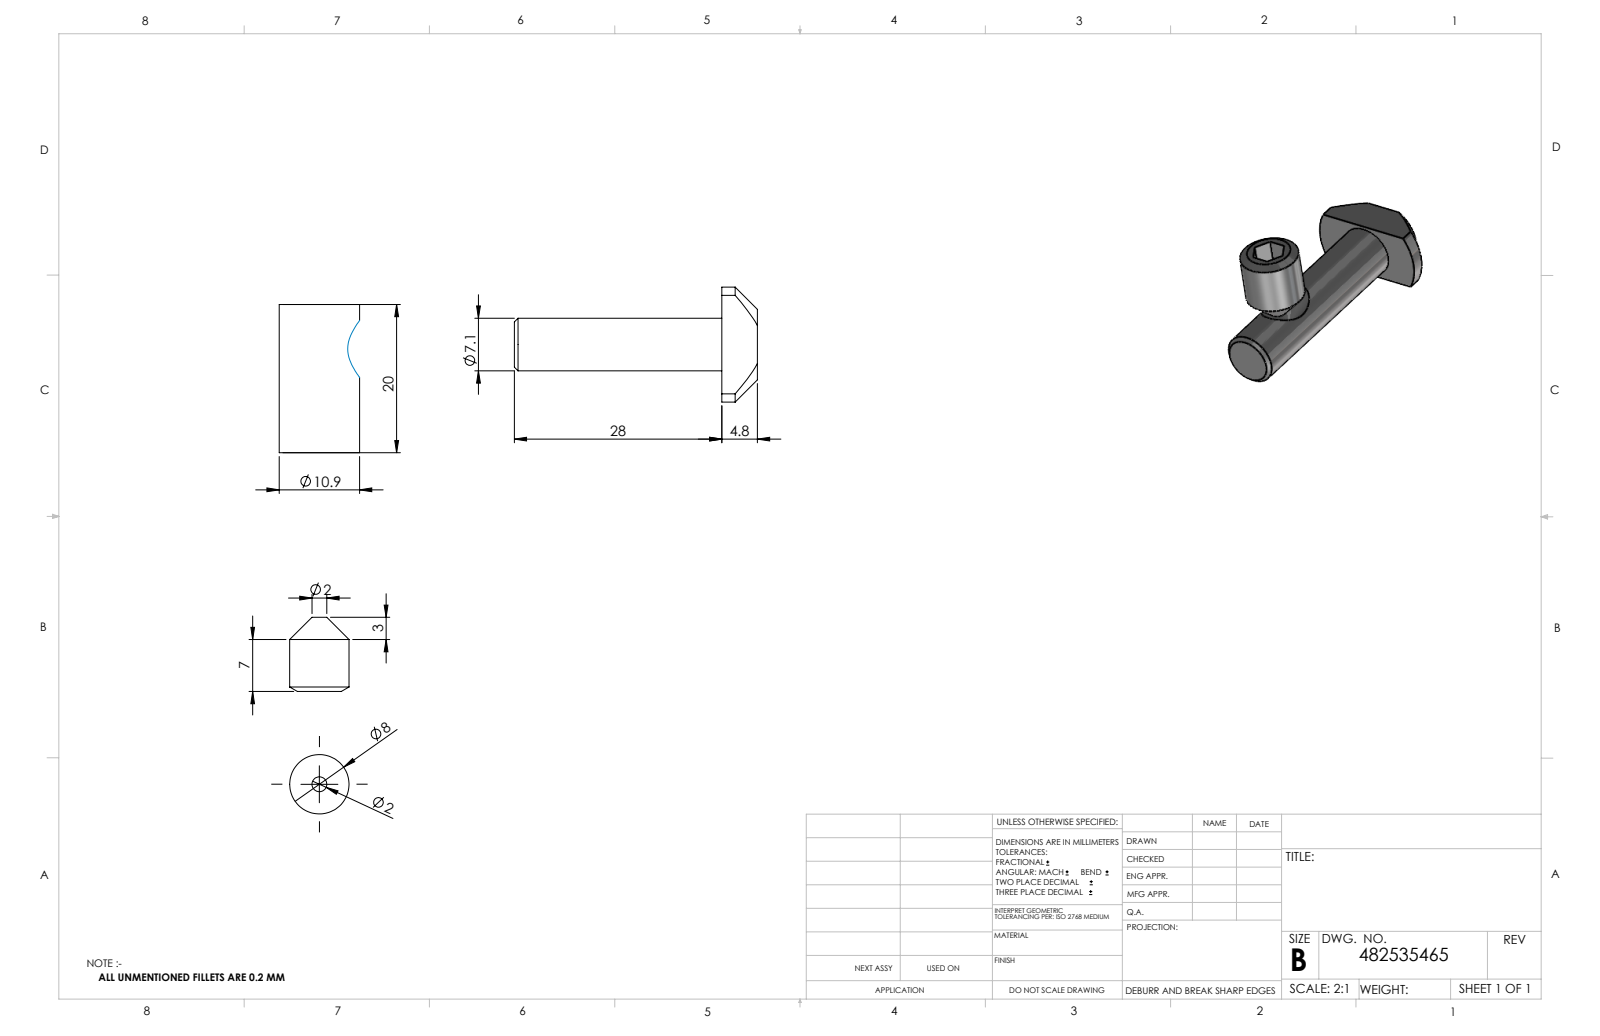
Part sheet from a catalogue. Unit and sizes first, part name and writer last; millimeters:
Units: millimetres
Overall size (bounding box): 32.8 × 20 × 15.5
Round holes (diameter × count): ⌀6.4 ×1, ⌀7.7 ×1
Round bosses / shafts (diameter × count): ⌀10.85 ×1, ⌀8 ×1, ⌀7.1 ×1
Partial cylindrical surfaces — rounded edges, fillets, slot ends (radius × count): R7.75 ×1
Main face-to-face distances: 10, 4.8, 2, 8, 4, 18, 20, 28, 32.8, 1
Volume: 2 916 mm³ · Surface area: 2 508 mm²
Bodies: 3 solids, 30 faces (16 planar, 7 cylindrical, 7 other)
Part name (STEP PRODUCT): 3842535465_Shrinkwrap_1
STEP written by: Autodesk Inventor 2019 (AUTOMOTIVE_DESIGN)
